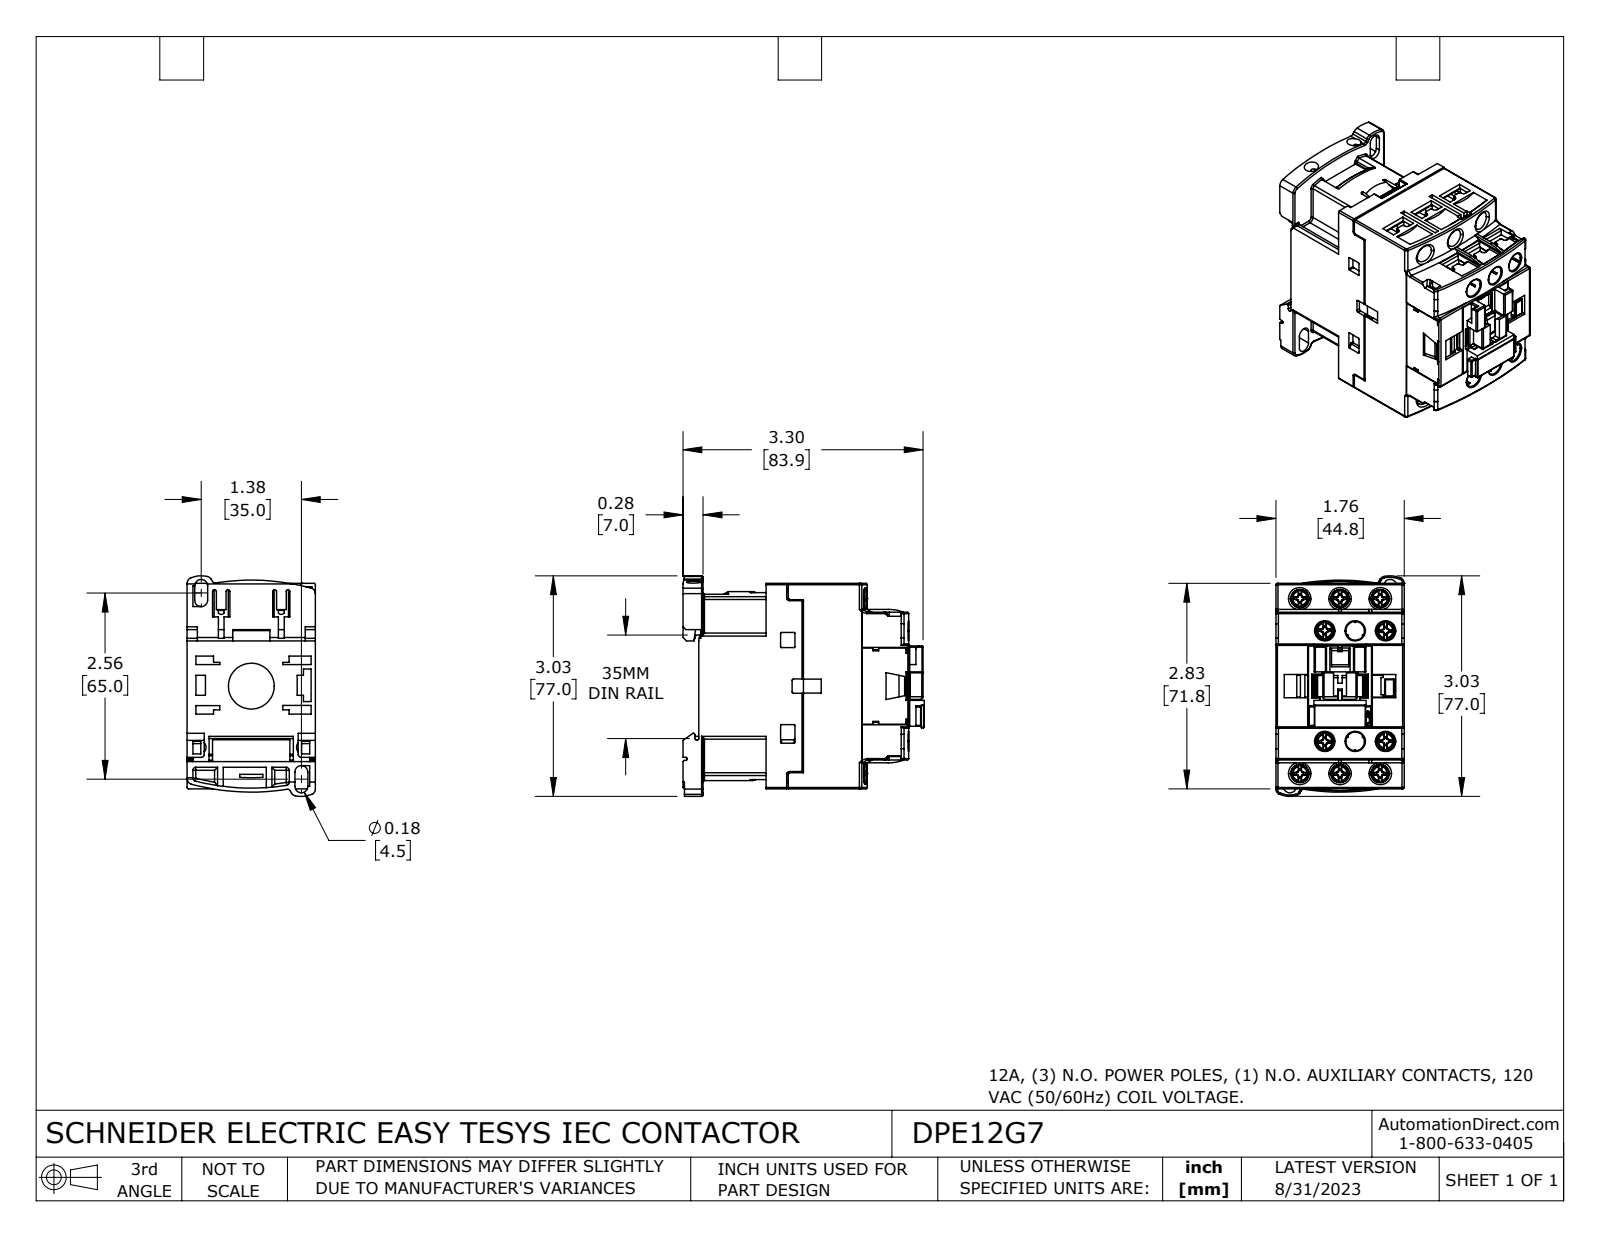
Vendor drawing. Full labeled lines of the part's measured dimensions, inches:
Part name (STEP PRODUCT): DPE12G7
STEP written by: SolidWorks 2021 (CONFIG_CONTROL_DESIGN)
Units: inches
Bodies: 20 solids, 3363 faces (2297 planar, 694 cylindrical, 372 other)
Overall size (bounding box): 3.317 × 3.031 × 1.783
Volume: 8.907 in³ · Surface area: 103.4 in²
Round holes (diameter × count): ⌀0.252 ×6, ⌀0.256 ×6, ⌀0.197 ×2, ⌀0.167 ×1, ⌀0.63 ×1
Round bosses / shafts (diameter × count): ⌀0.138 ×10, ⌀0.108 ×10, ⌀0.315 ×6
Partial cylindrical surfaces — rounded edges, fillets, slot ends (radius × count): R0.02 ×78, R0.012 ×64, R0.039 ×61, R0.006 ×42, R0.016 ×24, R0.63 ×9, R0.024 ×8, R0.079 ×7
Main face-to-face distances: 0.047, 1.764, 1.717, 0.321, 1.128, 0.807, 0.35, 2.78, 1.366, 1.118
Hole centre spacings: 0.417, 0.488, 0.551, 0.558, 0.788, 0.878, 1.321, 1.576
